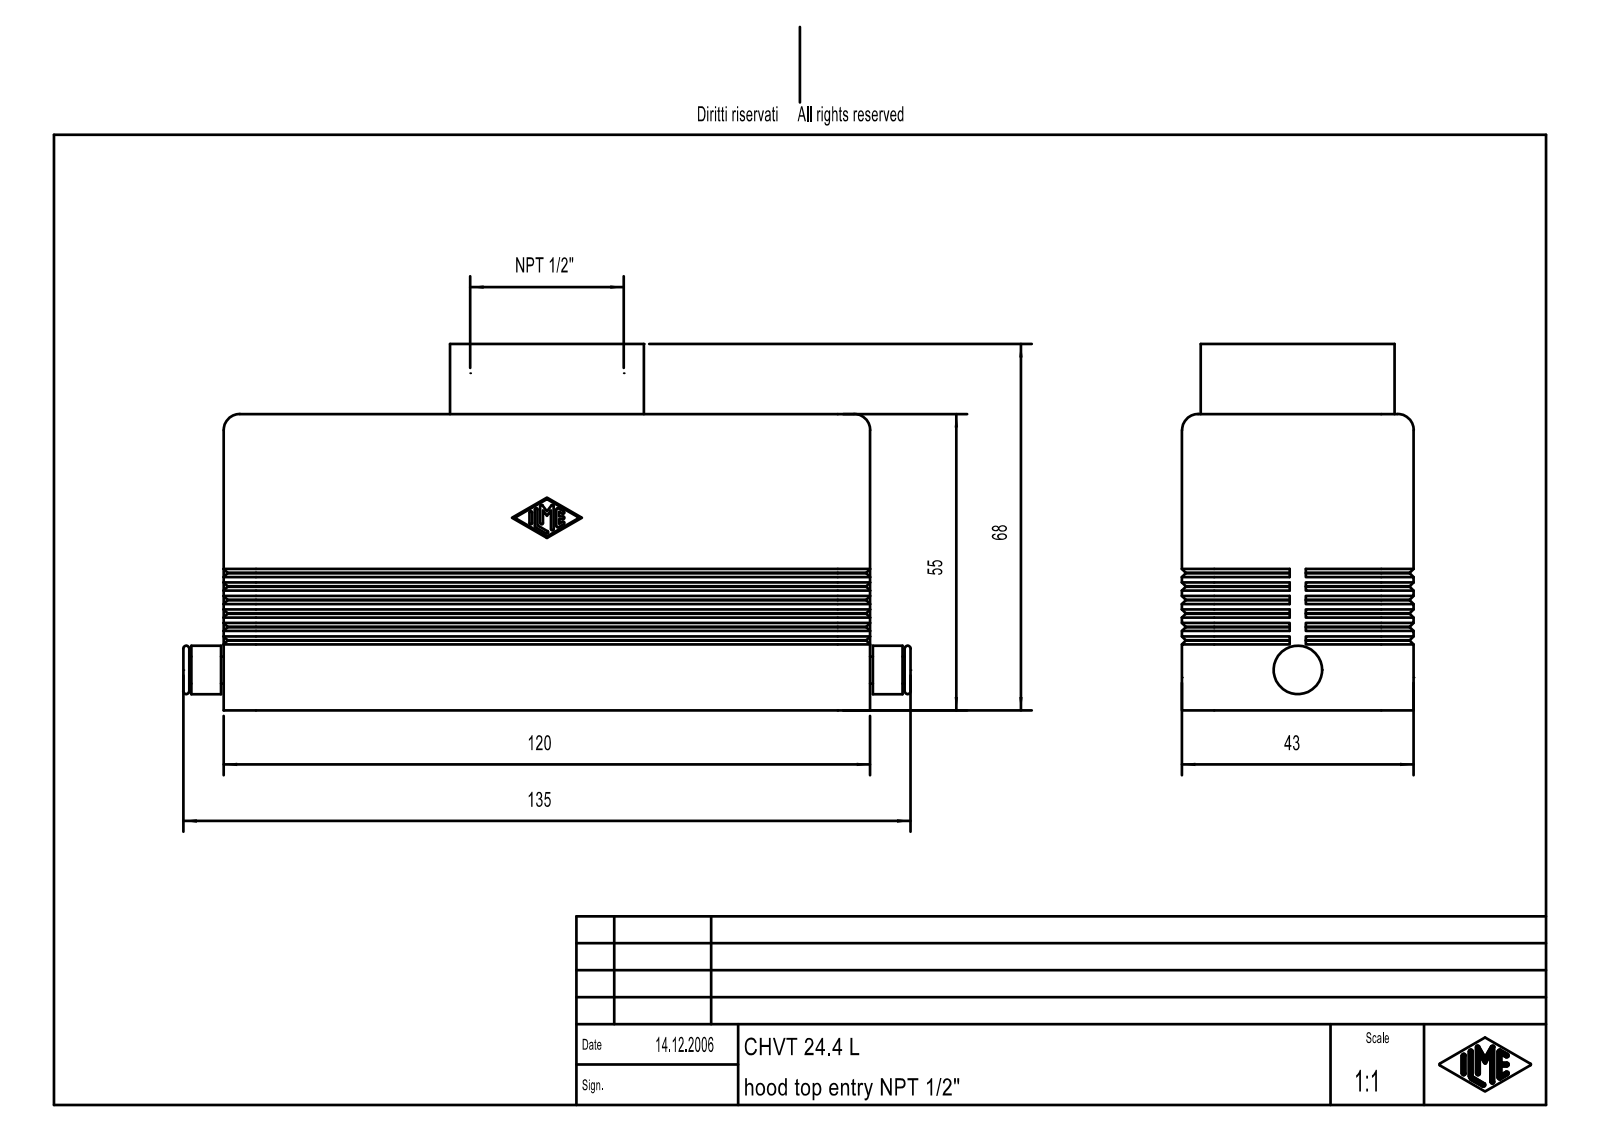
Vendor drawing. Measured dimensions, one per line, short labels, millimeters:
name: MSBO8121
written by: Creo Elements/Direct Modeling 18.0B 02-Dec-2011 (C) Parametric Technology GmbH (AUTOMOTIVE_DESIGN)
unit: mm
bodies: 1 solid, 399 faces (223 planar, 110 cylindrical, 66 other)
size: 135 × 68 × 43
volume: 84 040 mm³; area: 47 195 mm²
holes: 4× ⌀4, 2× ⌀2.46, 2× ⌀2.46
bosses: 1× ⌀36, 1× ⌀9, 1× ⌀5
rounds: 14× R0.25, 8× R3, 4× R2, 4× R5.3, 4× R6, 1× R1.5
face distances: 3, 40, 37, 43, 11.5, 8.5, 1.77, 117, 5.3, 20
hole spacings: 27, 104, 107.45
